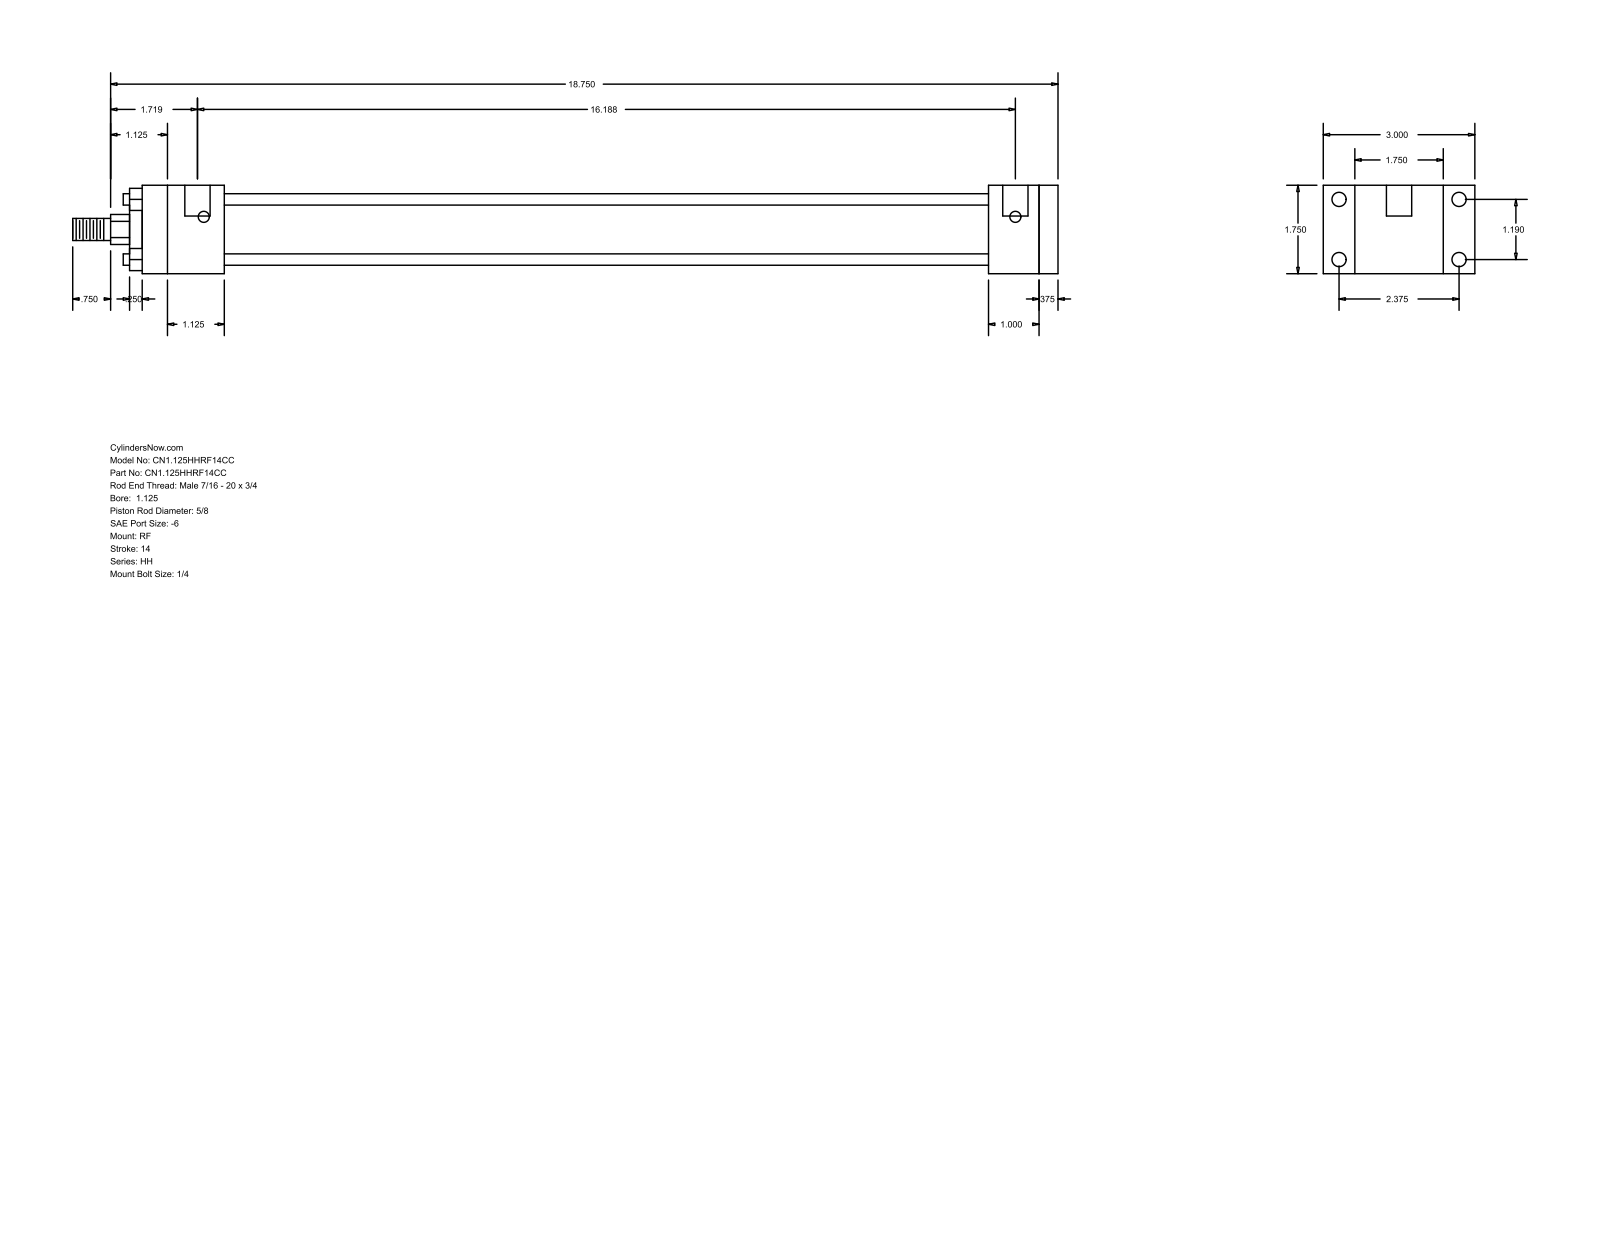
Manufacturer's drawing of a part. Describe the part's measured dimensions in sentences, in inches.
The part is named "HH_RF__0112_0.625". Its 3-D file was written by "GSSL Pune (CONFIG_CONTROL_DESIGN)". It is 0 solids with 92 faces: 64 planar, 28 cylindrical and 0 other. Overall it measures 19.5 by 3 by 1.75 inches. Round holes: 4 of diameter 0.219, 4 of diameter 0.281, 2 of diameter 0.5. Round bosses or shafts: 4 of diameter 0.225, 1 of diameter 1.375, 1 of diameter 1.125, 1 of diameter 0.625, 1 of diameter 0.437. Partial cylindrical surfaces (rounded edges, fillets, slot ends): 1 of radius 0.297. The main face-to-face distances are 1.75, 0.375, 1.375, 18.125, 0.625, 16.125, 16.5, 15.125, 1, 1.625. The hole center spacings are 1.19, 2.375, 2.656, 16.063, 0.125, 16.187.
